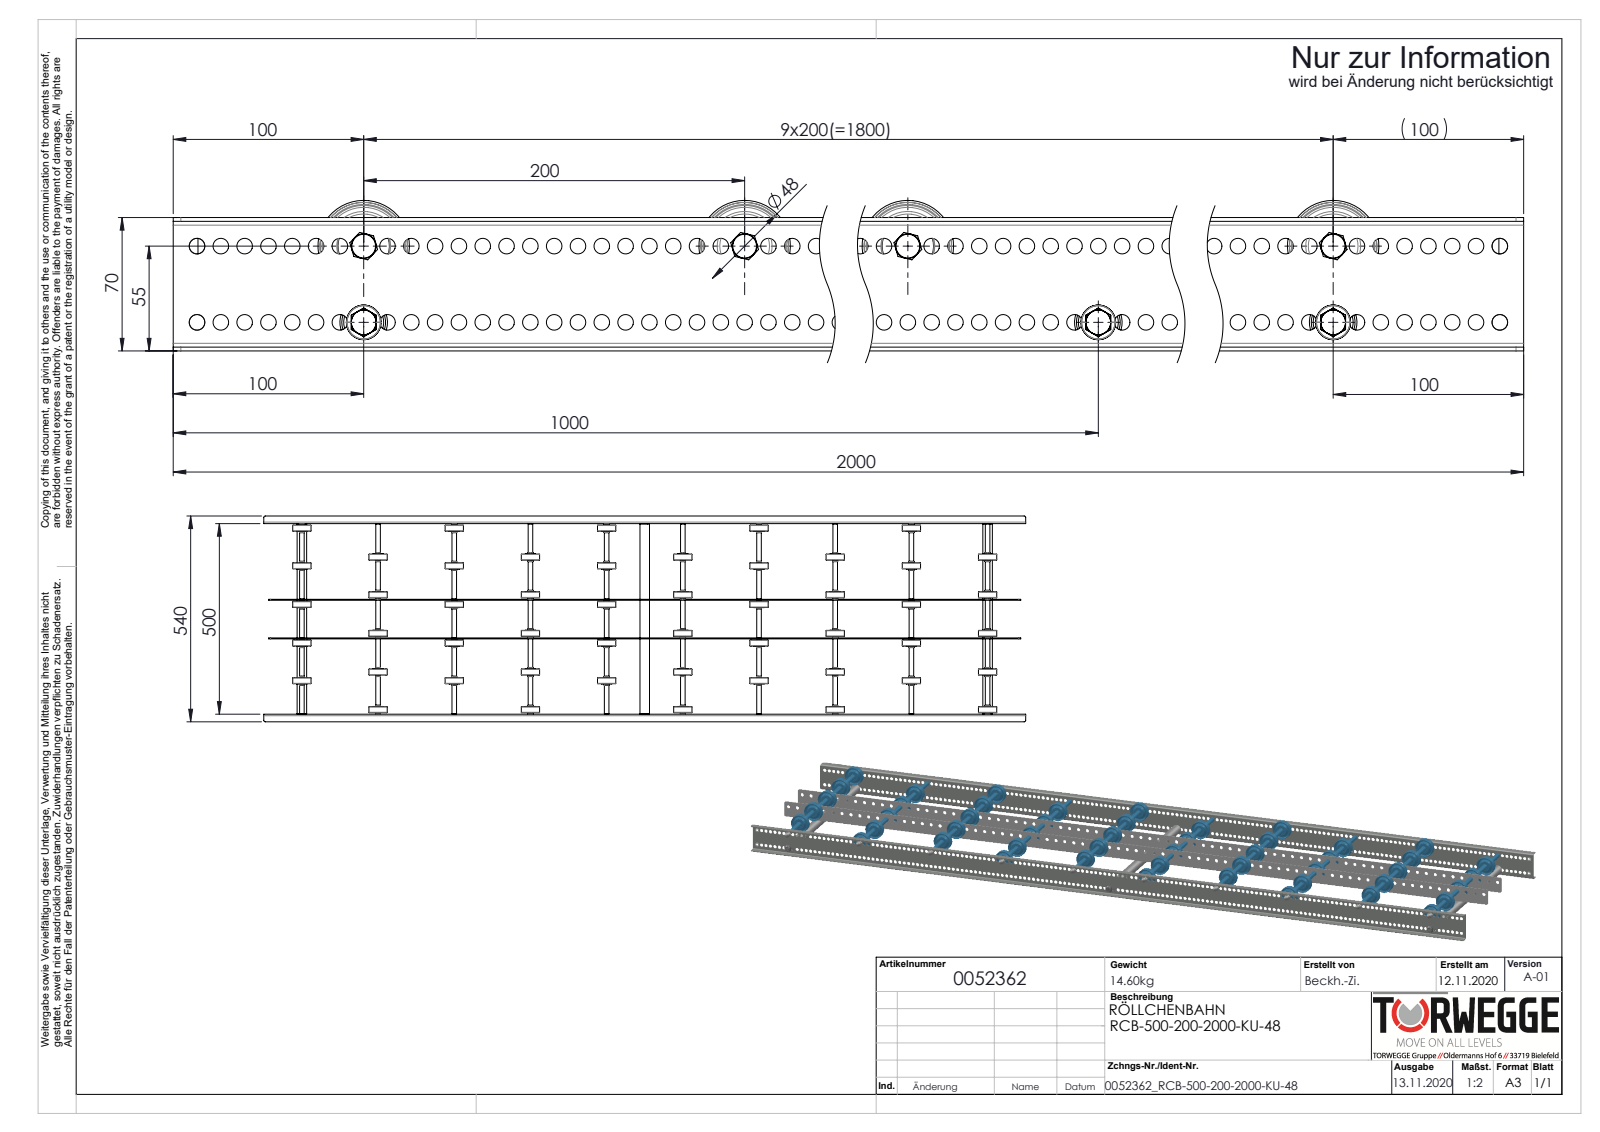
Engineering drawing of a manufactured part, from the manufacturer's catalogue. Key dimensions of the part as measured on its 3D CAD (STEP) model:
Part name (STEP PRODUCT): 0052362; Röllchenachse-für-Konfiguration_EL500; Profil_LRB-20x70x20x2_KFG_S100202_U-PROFIL-20-70-20-2-LRB-L=2000; S100100_Längstraverse-42x2,5_S100103_Lngstraverse-RB-L2000 (+6 more)
STEP written by: SolidWorks 2020 (AUTOMOTIVE_DESIGN)
Units: millimetres
Bodies: 149 solids, 6392 faces (1004 planar, 2872 cylindrical, 2516 other)
Overall size (bounding box): 2000 × 540 × 79
Volume: 2 791 000 mm³ · Surface area: 2 276 000 mm²
Round holes (diameter × count): ⌀8.2 ×318, ⌀8.5 ×79, ⌀6.65 ×10, ⌀9.65 ×10, ⌀13.7 ×10, ⌀6.8 ×3, ⌀21 ×3
Round bosses / shafts (diameter × count): ⌀8 ×13, ⌀48 ×10, ⌀27 ×10, ⌀12.7 ×10, ⌀12.5 ×10, ⌀12 ×10, ⌀25 ×3
Partial cylindrical surfaces — rounded edges, fillets, slot ends (radius × count): R4 ×8, R2 ×4, R5 ×4
Main face-to-face distances: 2, 502, 101.3, 2.5, 68, 504, 500, 200.1, 301.4, 98.8
Hole centre spacings: 12.5, 25, 37.5, 50, 62.5, 75, 87.5, 100
